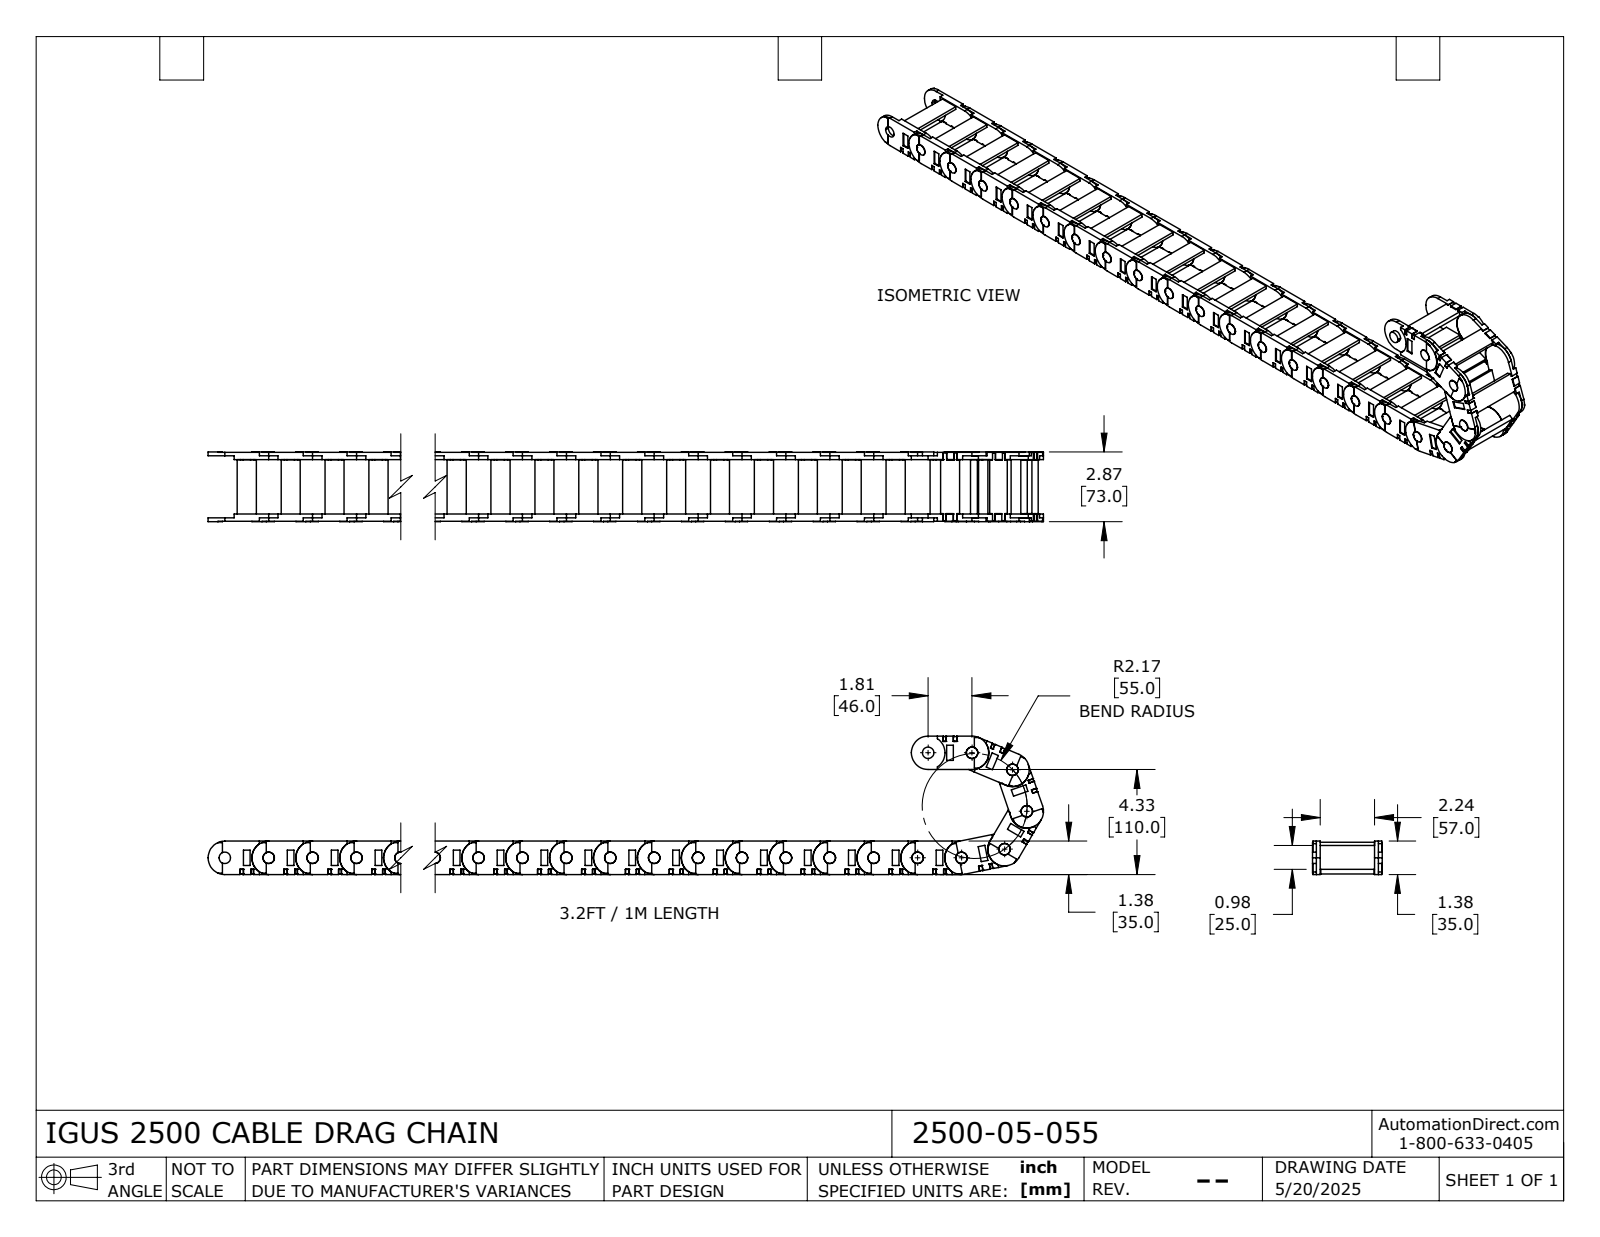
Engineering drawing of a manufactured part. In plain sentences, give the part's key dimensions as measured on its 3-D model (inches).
The part is named "2500_05_055". Its 3-D file was written by "SolidWorks 2024 (AUTOMOTIVE_DESIGN)". It is 66 solids with 2398 faces: 1870 planar, 528 cylindrical and 0 other. Overall it measures 34.858 by 5.709 by 2.874 inches. Its volume is 45.18 cubic inches and its surface area 663.9 square inches. Round holes: 22 of diameter 0.473. Round bosses or shafts: 22 of diameter 0.472, 21 of diameter 1.378. Partial cylindrical surfaces (rounded edges, fillets, slot ends): 23 of radius 0.697, 2 of radius 0.689. The main face-to-face distances are 0.157, 2.402, 2.559, 0.142, 0.299, 2.543, 2.701, 2.244, 0.197, 0.134. The hole center spacings are 1.811, 3.622, 5.433, 7.244, 9.055, 10.866, 12.677, 14.488.
